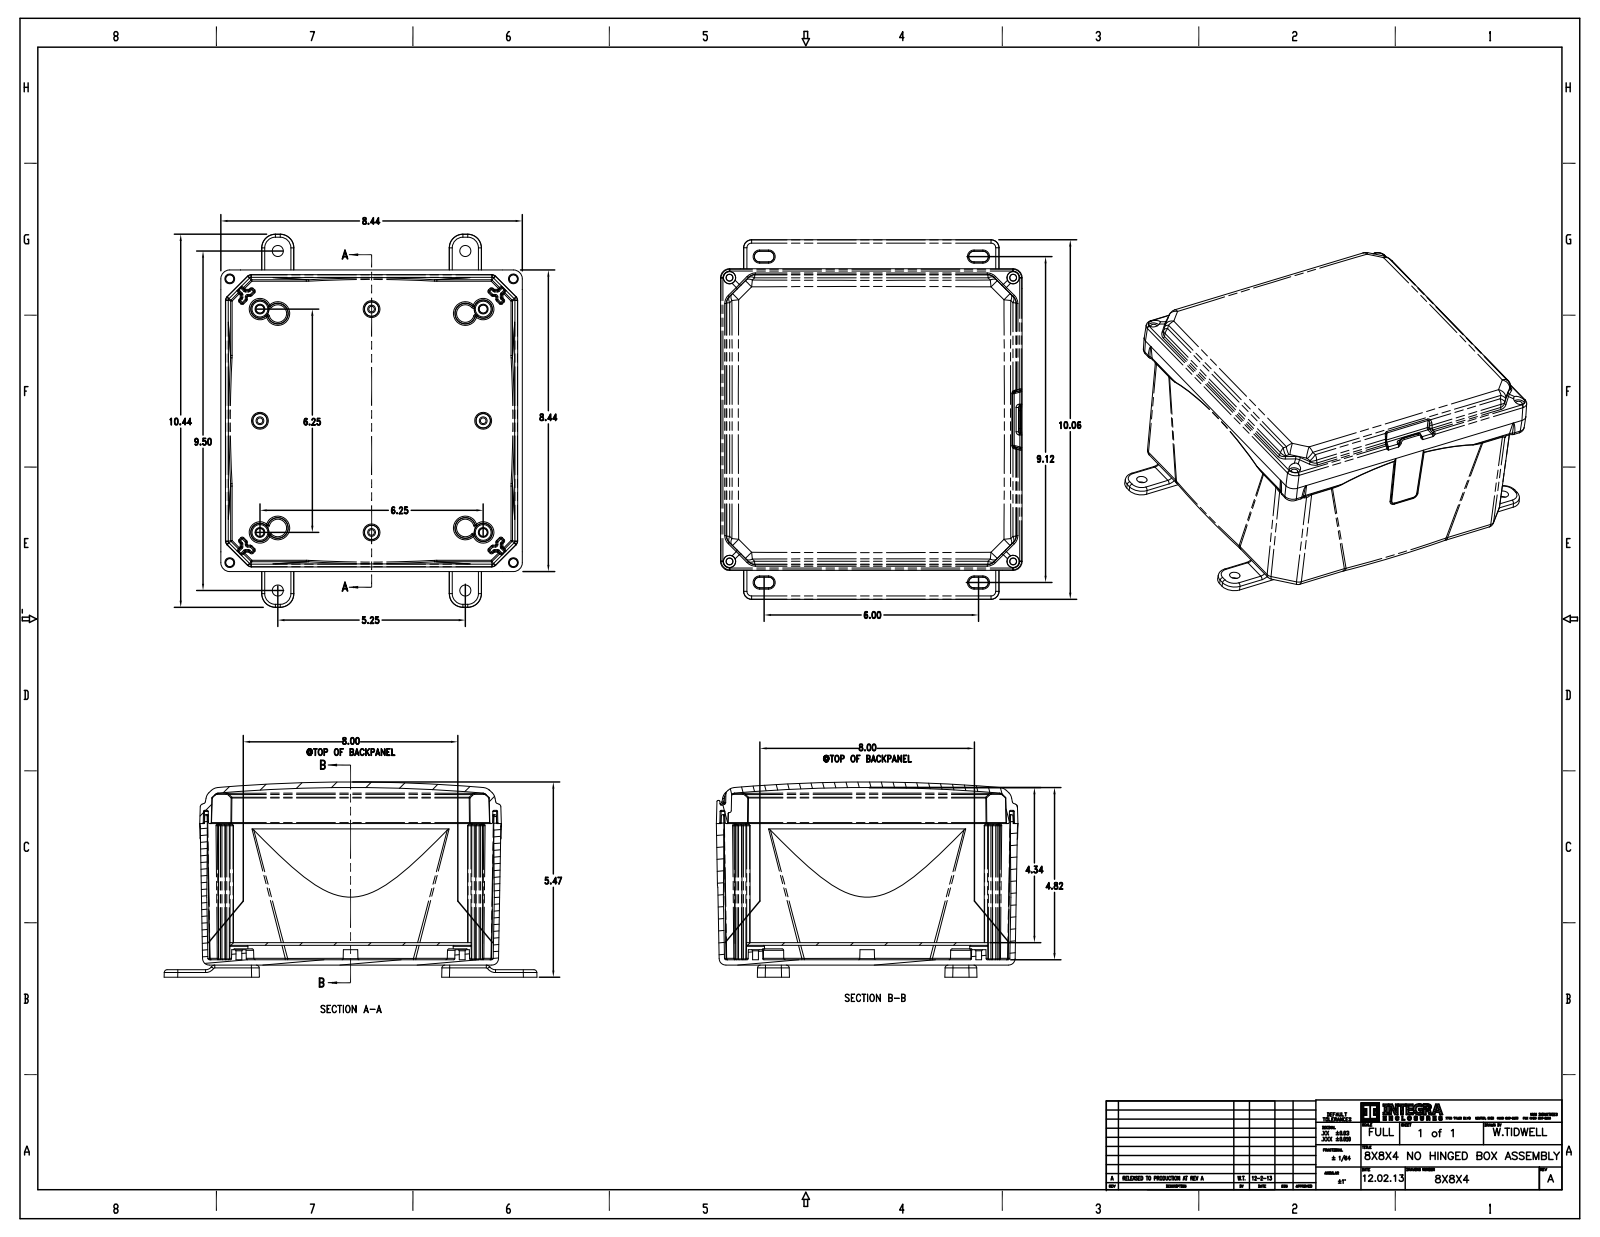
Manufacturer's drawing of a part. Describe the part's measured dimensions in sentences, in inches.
The part is named "H884BS; 9912525-80-10; 9912521-80-10; H884BS_ASM (+5 more)". Its 3-D file was written by "CREO PARAMETRIC BY PTC INC, 2016050 (CONFIG_CONTROL_DESIGN)". It is 25 solids with 3473 faces: 793 planar, 1440 cylindrical and 1240 other. Overall it measures 10.06 by 8.44 by 5.465 inches. Its volume is 52.86 cubic inches and its surface area 749 square inches. Round holes: 8 of diameter 0.19, 4 of diameter 0.16, 4 of diameter 0.201. Round bosses or shafts: 12 of diameter 0.25, 8 of diameter 0.3, 8 of diameter 0.298, 8 of diameter 0.29, 8 of diameter 0.26, 8 of diameter 0.258, 4 of diameter 0.375, 4 of diameter 0.372. Partial cylindrical surfaces (rounded edges, fillets, slot ends): 314 of radius 0.03, 91 of radius 0.02, 60 of radius 0.025, 48 of radius 0.005, 46 of radius 0.09, 37 of radius 0.06, 31 of radius 0.08, 28 of radius 0.25. The main face-to-face distances are 0.15, 0.12, 0.32, 0.27, 0.34, 0.225, 0.49, 0.13, 0.095, 0.22. The hole center spacings are 3.125, 4.059, 6.988, 7.145, 8.13, 6.25, 0.516, 1.195.
